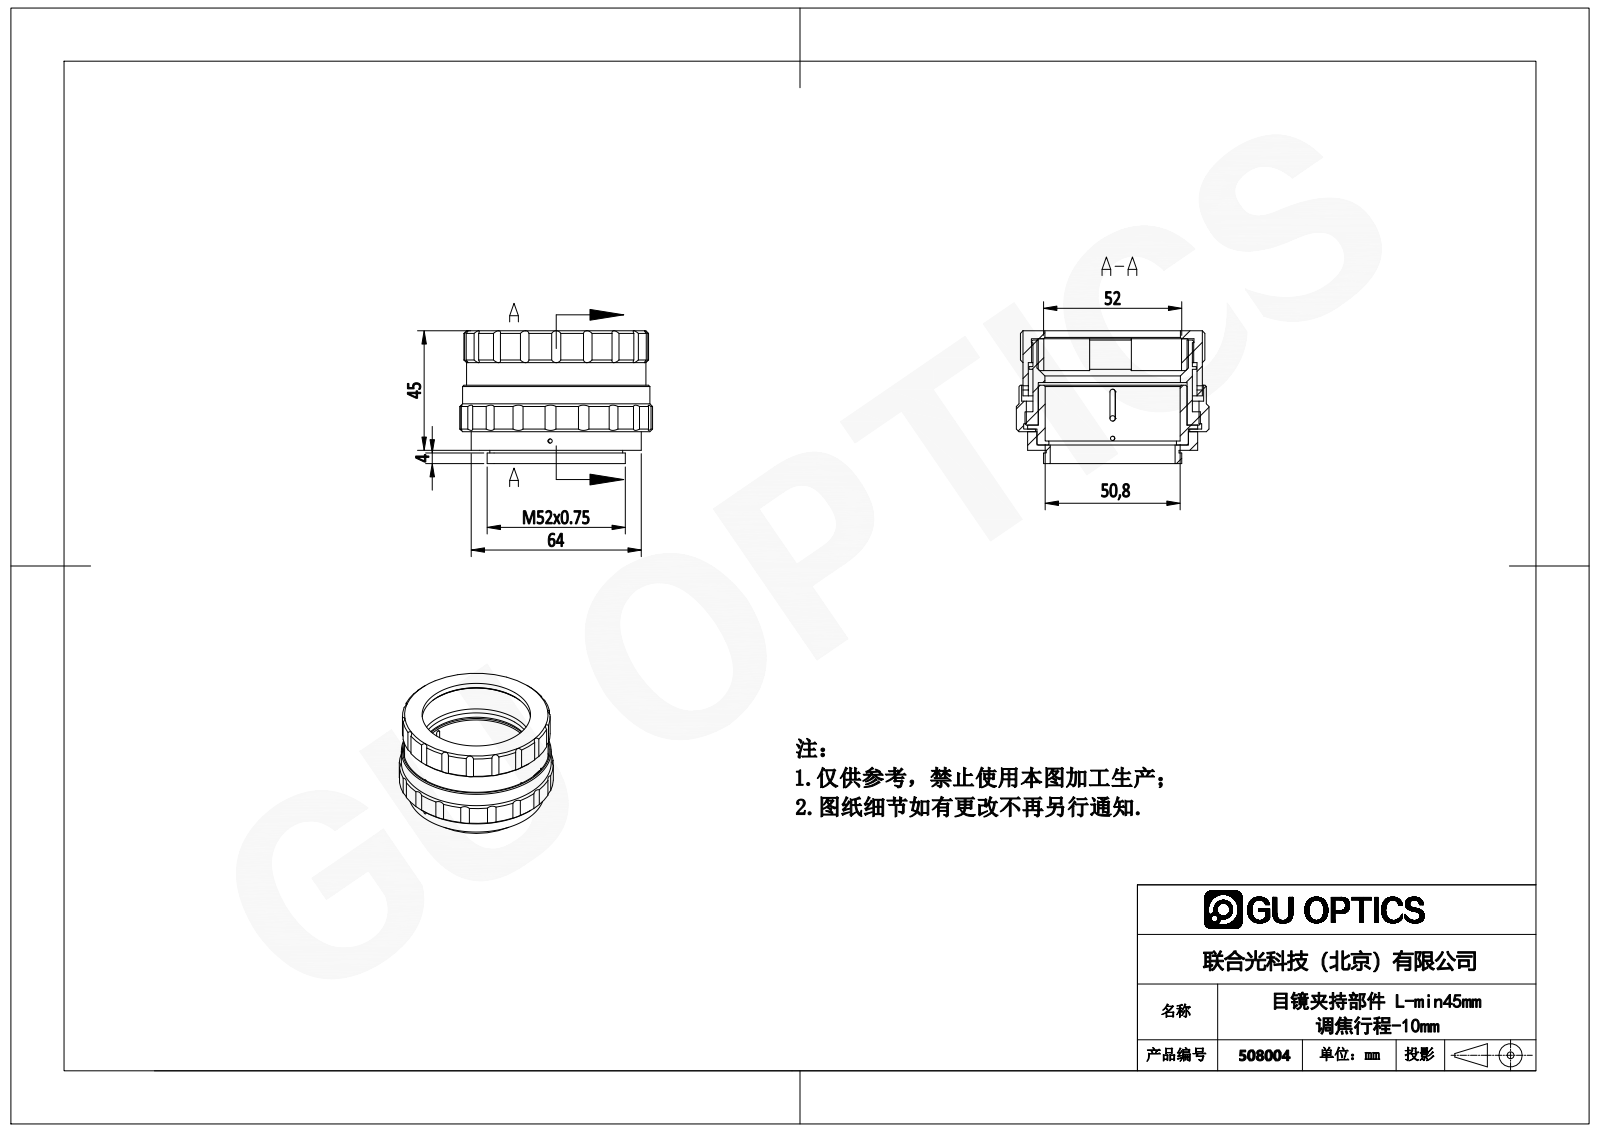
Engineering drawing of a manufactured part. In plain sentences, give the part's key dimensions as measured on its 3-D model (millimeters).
The part is named "508004". Its 3-D file was written by "SolidWorks 2020 (CONFIG_CONTROL_DESIGN)". It is 6 solids with 274 faces: 35 planar, 180 cylindrical and 59 other. Overall it measures 72.5 by 72.5 by 50 millimeters. Its volume is 69 968 cubic millimeters and its surface area 61 296 square millimeters. Round holes: 7 of diameter 1.6, 1 of diameter 2.05, 1 of diameter 47, 1 of diameter 48, 1 of diameter 50.8, 1 of diameter 51, 1 of diameter 51.85, 1 of diameter 56, 1 of diameter 58, 1 of diameter 61.2, 1 of diameter 63.5, 1 of diameter 65. Round bosses or shafts: 1 of diameter 70.5, 1 of diameter 67.5, 1 of diameter 66, 1 of diameter 64, 1 of diameter 63, 1 of diameter 61, 1 of diameter 60, 1 of diameter 57. Partial cylindrical surfaces (rounded edges, fillets, slot ends): 18 of radius 2, 18 of radius 5, 2 of radius 1, 1 of radius 34.75, 1 of radius 36.25. The main face-to-face distances are 5, 6, 7.5, 7, 1.5, 1, 23.5, 38, 2.5, 2.
